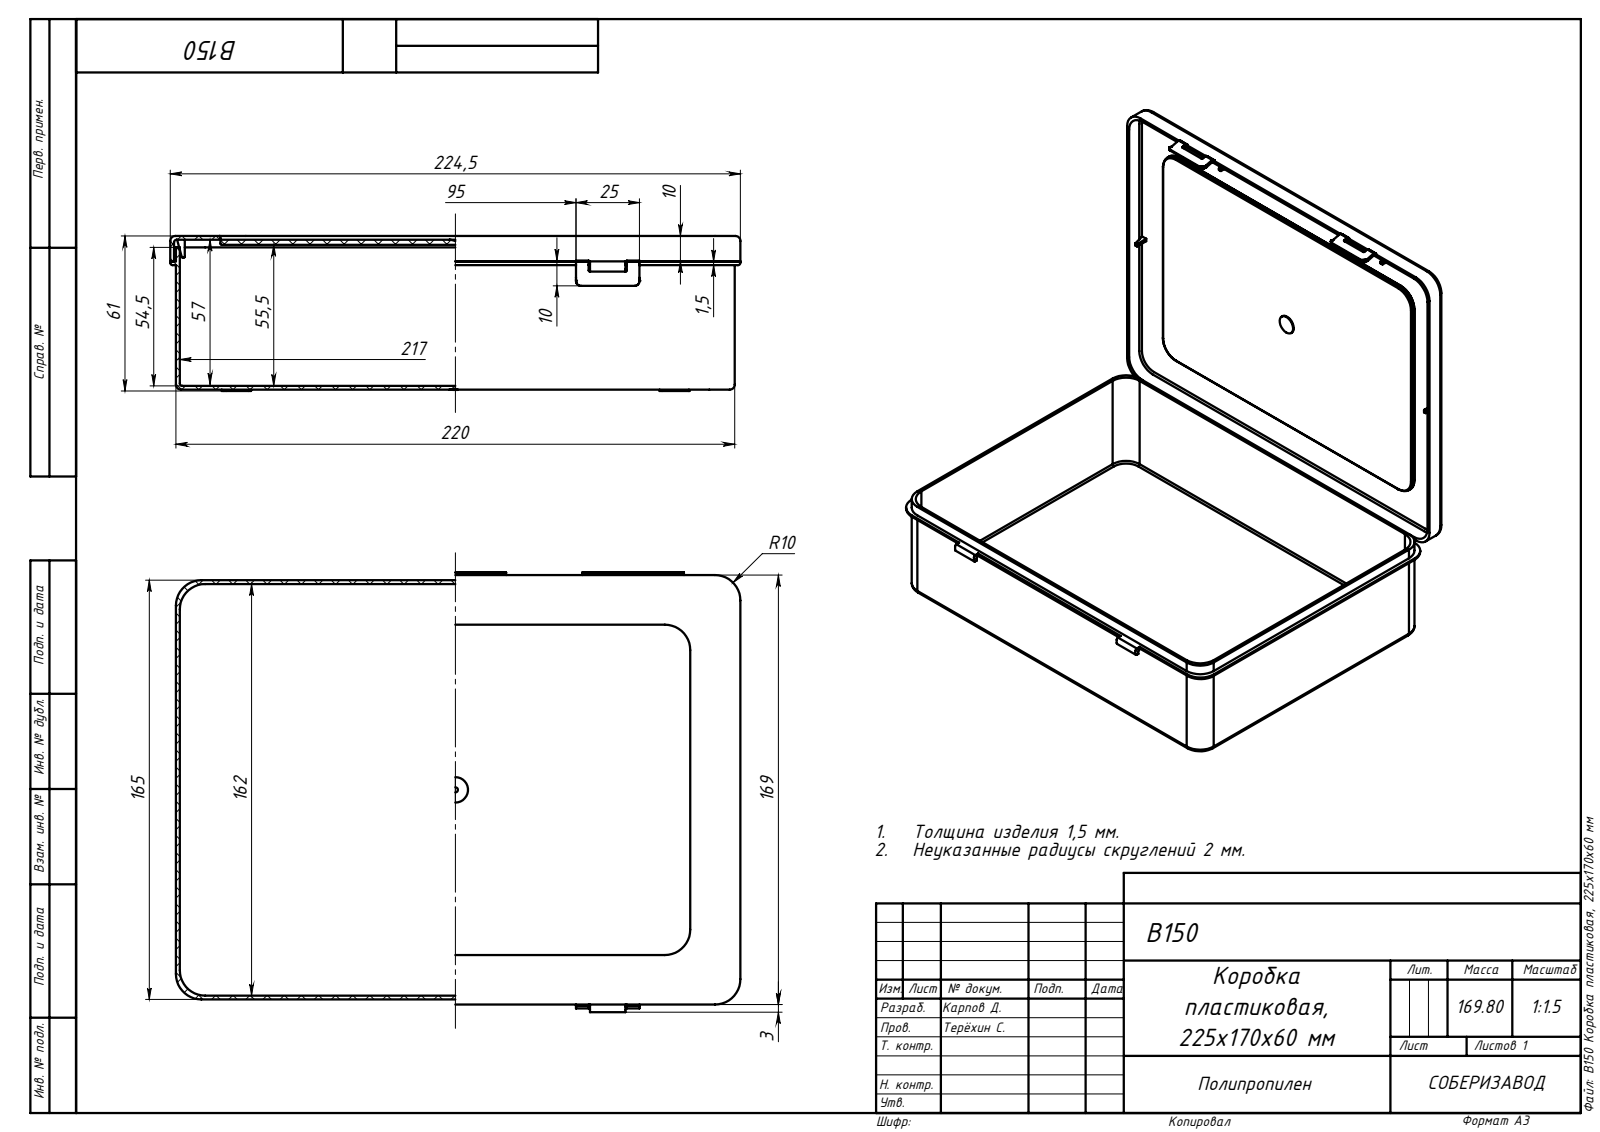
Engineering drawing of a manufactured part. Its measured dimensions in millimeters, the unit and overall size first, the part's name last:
Units: millimetres
Overall size (bounding box): 224.5 × 173 × 61
Round bosses / shafts (diameter × count): ⌀10 ×1, ⌀2 ×1
Partial cylindrical surfaces — rounded edges, fillets, slot ends (radius × count): R1 ×31, R10 ×24, R0.3 ×20, R0.5 ×17, R2 ×12, R11.5 ×4, R0.1 ×1
Main face-to-face distances: 1.5, 59, 57.5, 2, 57, 55.5, 163.5, 3.5, 218.5, 60.5
Volume: 197 732 mm³ · Surface area: 249 832 mm²
Bodies: 6 solids, 347 faces (160 planar, 155 cylindrical, 32 other)
Part name (STEP PRODUCT): B150 Защёлка_00; B150 Коробка пластиковая, 225x170x60 мм; B150 Емкость; B150 Крышка
STEP written by: SolidWorks 2020 (AUTOMOTIVE_DESIGN)
